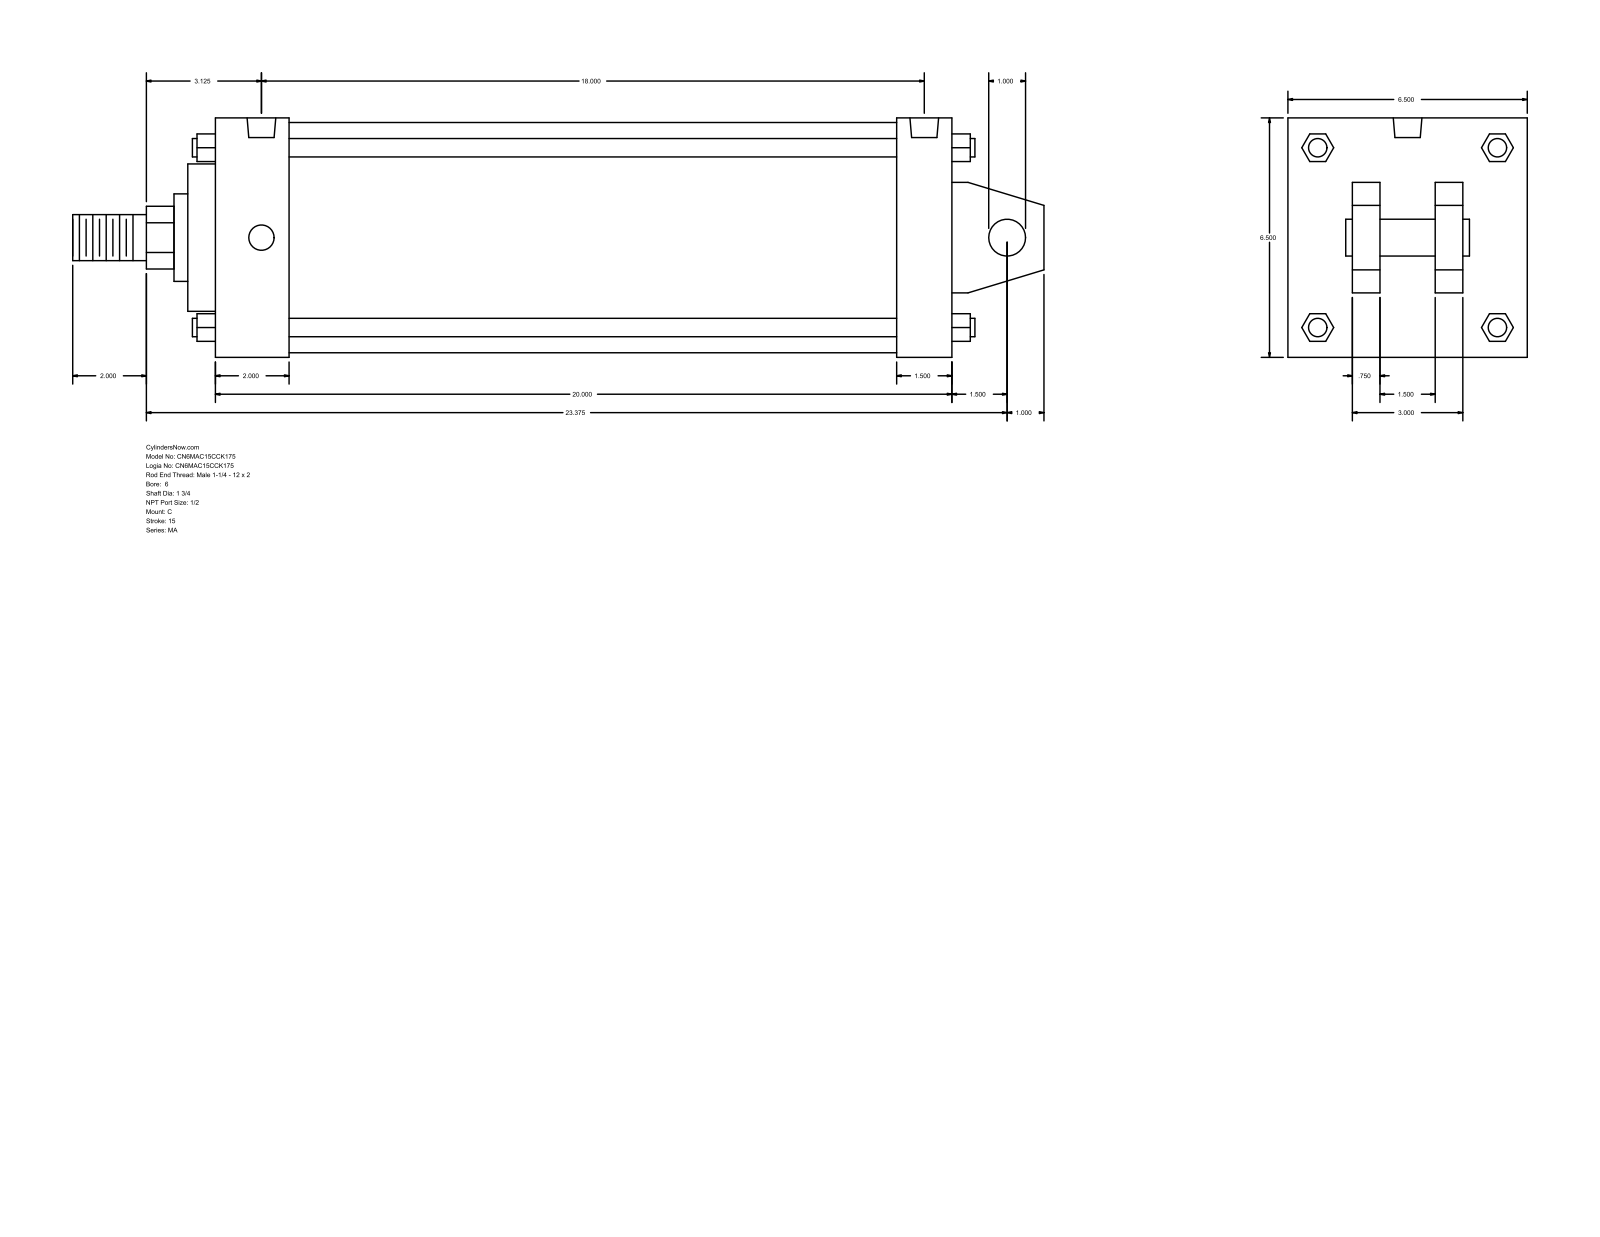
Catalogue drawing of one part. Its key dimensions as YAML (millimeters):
part_name: "MA_C__0600_1.75"
step_written_by: "GSSL Pune (CONFIG_CONTROL_DESIGN)"
units: millimeters
bodies: {solids: 0, faces: 141, planar: 109, cylindrical: 32, other: 0}
overall_size: [669.92, 165.1, 165.1]
round_holes:
  - {diameter: 17.46, count: 4}
  - {diameter: 19.77, count: 2}
round_bosses_or_shafts:
  - {diameter: 12.7, count: 4}
  - {diameter: 158.75, count: 1}
  - {diameter: 101.6, count: 1}
  - {diameter: 60.33, count: 1}
  - {diameter: 44.45, count: 1}
  - {diameter: 31.75, count: 1}
  - {diameter: 25.4, count: 1}
partial_cylinders:
  - {radius: 21.63, count: 1}
face_to_face_distances: [165.1, 508, 19.05, 38.1, 63.5, 101.6, 44.45, 120.65, 57.15, 50.8]
hole_center_spacings: [457.2]
